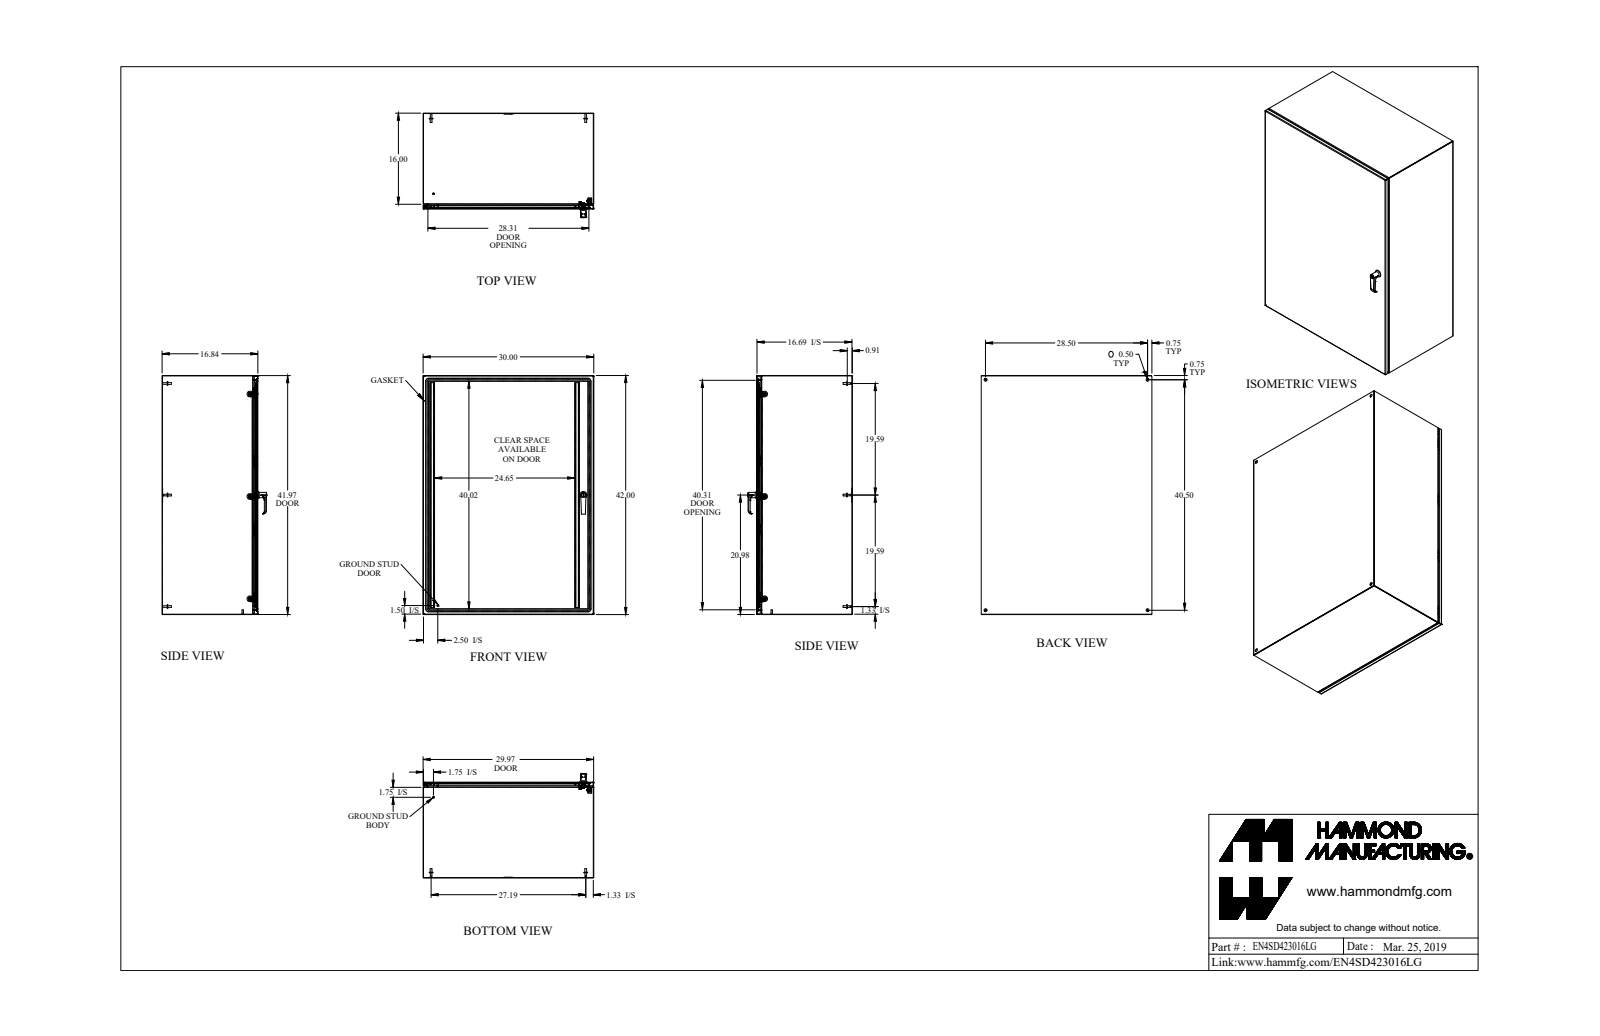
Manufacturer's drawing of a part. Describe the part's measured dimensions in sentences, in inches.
The part is named "EN4SD423016LG". Its 3-D file was written by "SolidWorks 2019 (AUTOMOTIVE_DESIGN)". It is 55 solids with 1443 faces: 632 planar, 532 cylindrical and 279 other. Overall it measures 42 by 30 by 18.367 inches. Its volume is 395.3 cubic inches and its surface area 10 974 square inches. Round holes: 6 of diameter 0.176, 4 of diameter 0.5, 3 of diameter 0.196, 3 of diameter 0.25, 3 of diameter 0.265, 3 of diameter 0.413, 2 of diameter 0.256, 2 of diameter 0.313, 2 of diameter 0.394, 1 of diameter 0.172, 1 of diameter 0.24, 1 of diameter 0.242. Round bosses or shafts: 7 of diameter 0.25, 6 of diameter 0.625, 6 of diameter 0.375, 6 of diameter 0.313, 6 of diameter 0.27, 6 of diameter 0.156, 3 of diameter 1, 2 of diameter 0.63. Partial cylindrical surfaces (rounded edges, fillets, slot ends): 18 of radius 0.036, 18 of radius 0.108, 15 of radius 0.03, 12 of radius 0.043, 12 of radius 0.081, 8 of radius 0.006, 8 of radius 0.048, 8 of radius 0.062. The main face-to-face distances are 0.072, 16.765, 29.928, 16.693, 16.837, 41.928, 29.856, 30, 41.856, 42. The hole center spacings are 0.787, 2.507, 17.981, 17.988, 18, 27.52, 28.5, 35.969.
